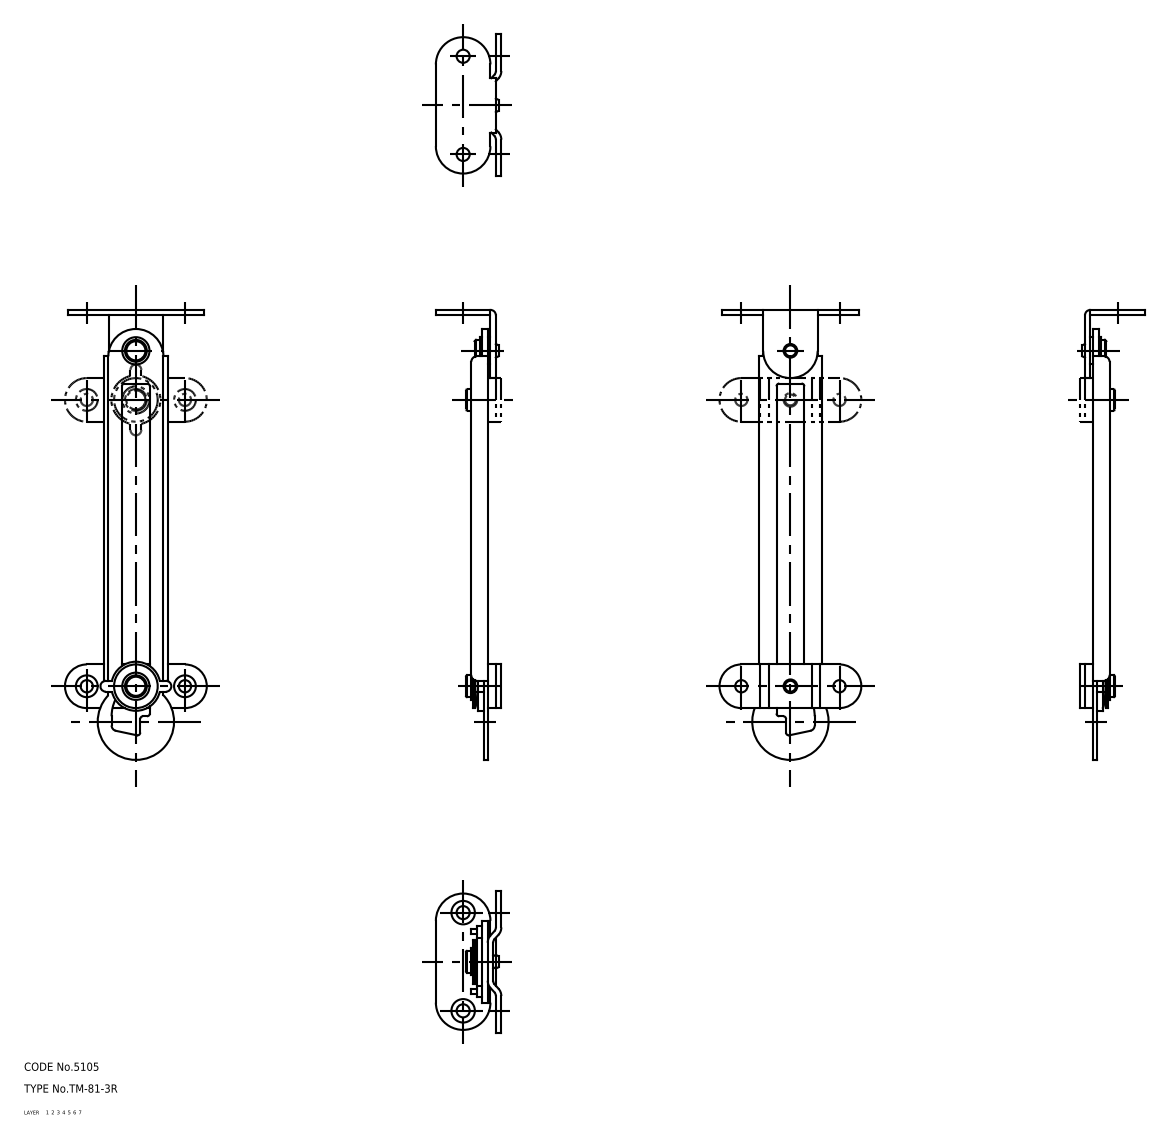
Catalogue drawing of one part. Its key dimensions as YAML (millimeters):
part_name: "67118481; 67118494; 67118507; 67118520 (+7 more)"
step_written_by: "CADfix (AUTOMOTIVE_DESIGN)"
units: millimeters
bodies: {solids: 11, faces: 160, planar: 0, cylindrical: 0, other: 160}
overall_size: [165, 52, 24]
volume: 10143
surface_area: 14805
